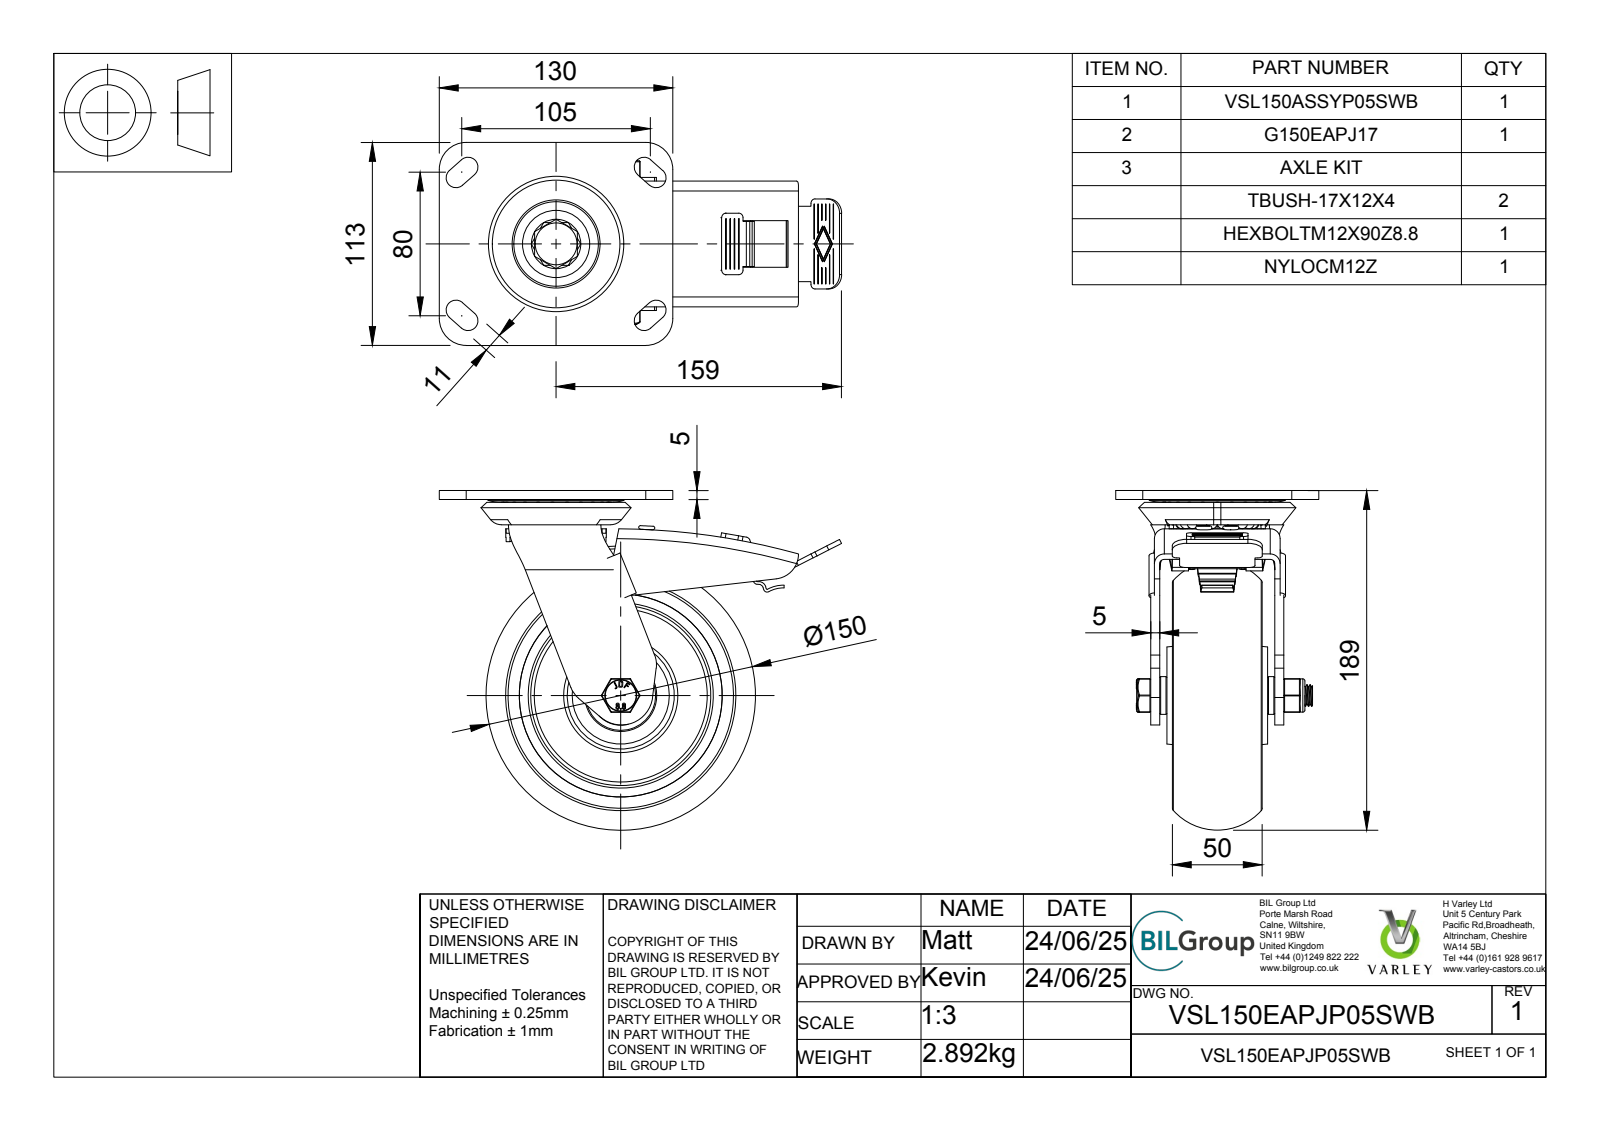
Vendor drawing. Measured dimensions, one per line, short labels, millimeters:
name: VSL150EAPJP05SWB v3; G150EAPJ17 v2; RIM; TYRE (+8 more)
written by: Autodesk Translation Framework v14.10.0.0 (AUTOMOTIVE_DESIGN)
unit: mm
bodies: 85 solids, 1102 faces (484 planar, 322 cylindrical, 296 other)
size: 223.98 × 189.11 × 113
volume: 775 070 mm³; area: 272 667 mm²
holes: 4× ⌀5.2, 1× ⌀12, 1× ⌀12.2, 1× ⌀13, 1× ⌀14, 1× ⌀16.3, 1× ⌀16.5, 1× ⌀17, 1× ⌀24.5, 1× ⌀25, 1× ⌀32.53, 1× ⌀32.7
bosses: 2× ⌀5, 1× ⌀56, 1× ⌀32.73, 1× ⌀25.2, 1× ⌀21, 1× ⌀18.5, 1× ⌀17.75, 1× ⌀16.8
rounds: 28× R3, 23× R0.5, 21× R1, 16× R2.5, 8× R0.9, 8× R5.5, 6× R6, 6× R15
face distances: 5, 7, 12, 69, 34, 40, 29, 35, 62, 57
hole spacings: 15
